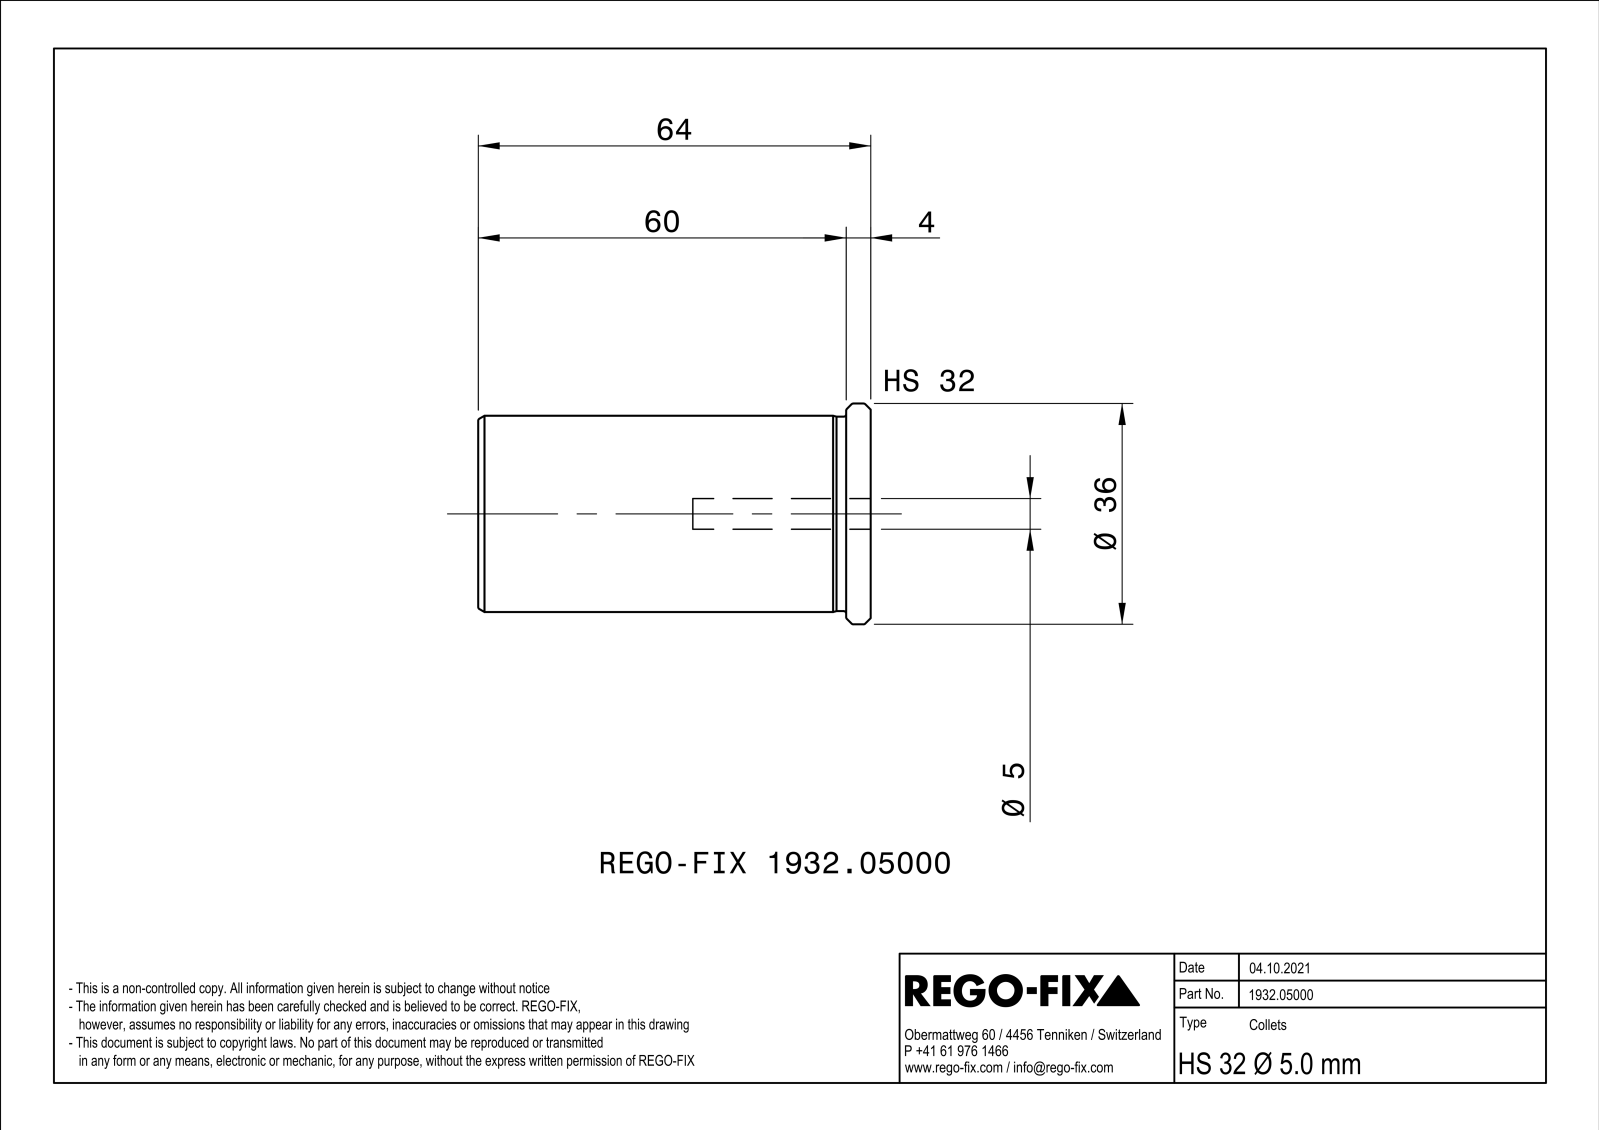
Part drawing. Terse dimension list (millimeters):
name: NOCUT
written by: SIEMENS PLM Software Solid Edge ST10 (AUTOMOTIVE_DESIGN)
unit: mm
bodies: 1 solid, 75 faces (22 planar, 12 cylindrical, 41 other)
size: 64 × 35.99 × 35.99
volume: 39 659 mm³; area: 14 135 mm²
holes: 1× ⌀5, 1× ⌀10, 1× ⌀26.5
bosses: 1× ⌀36, 1× ⌀32, 1× ⌀31.7
face distances: 1, 64, 4, 60
